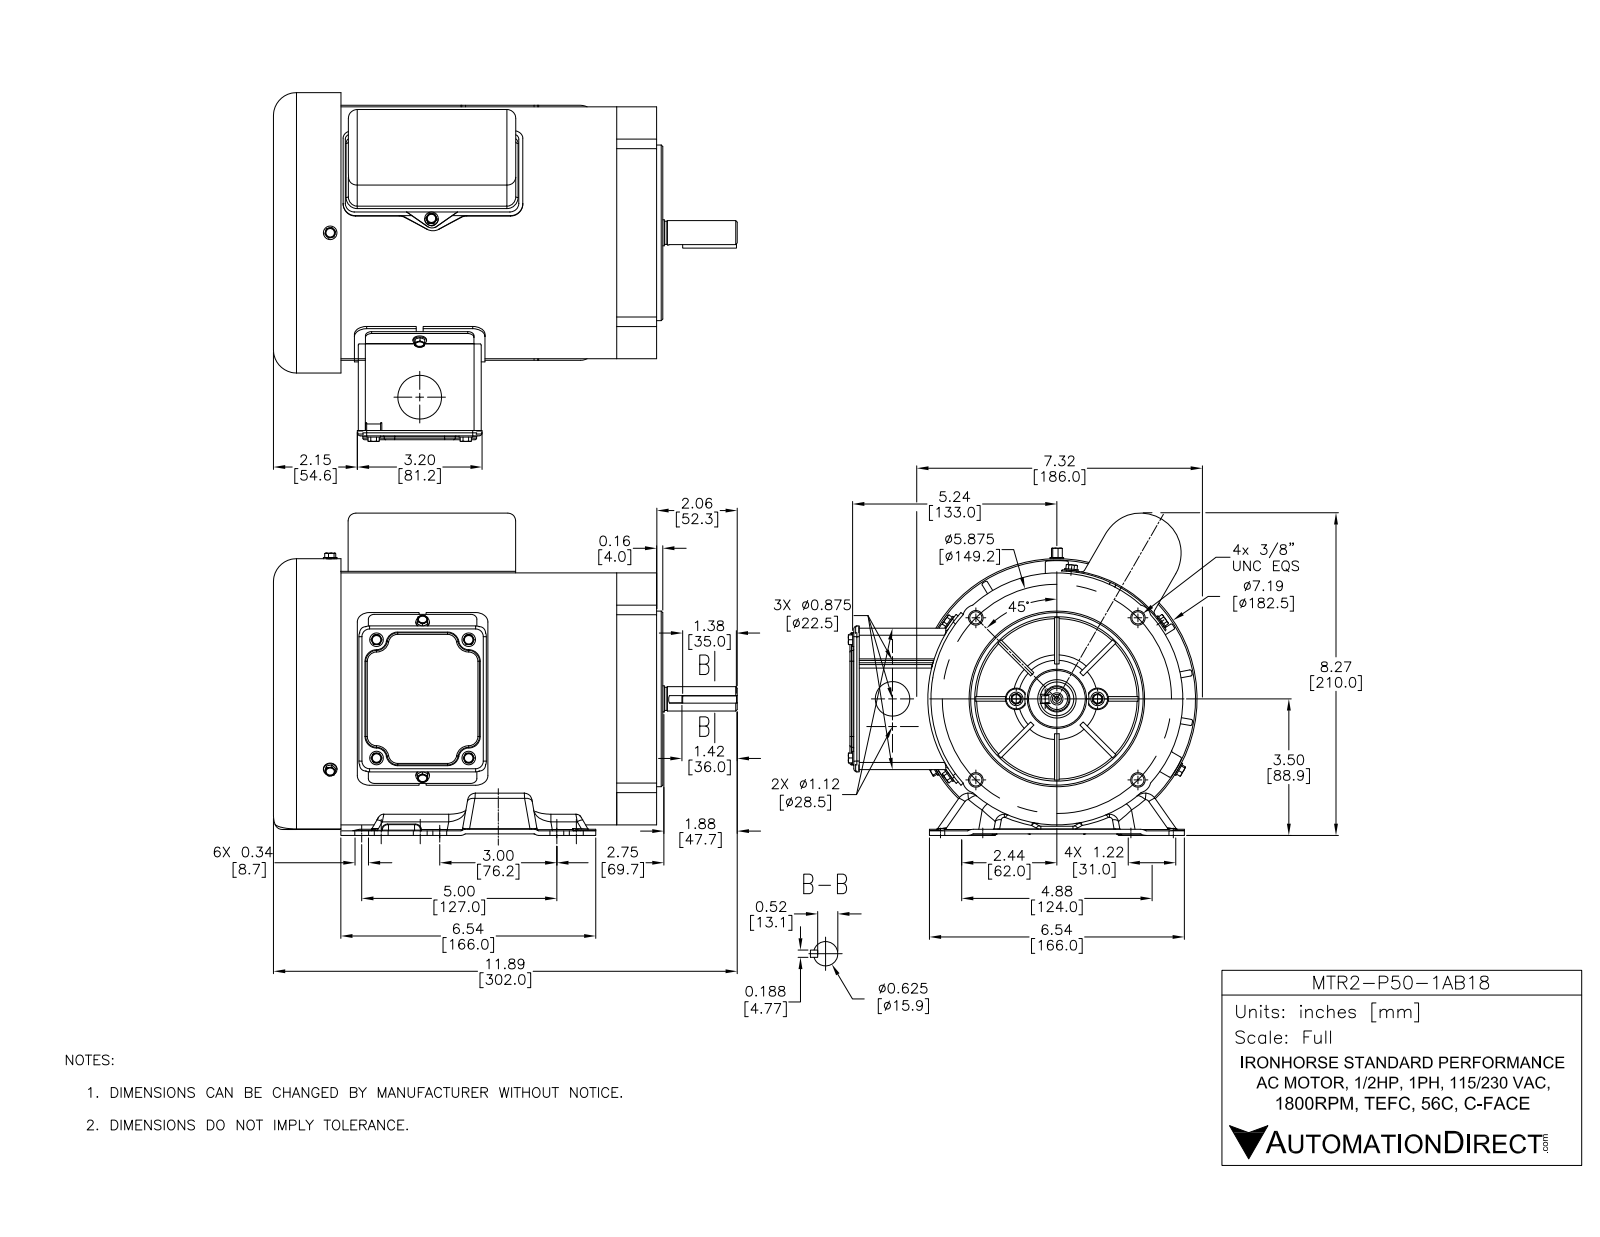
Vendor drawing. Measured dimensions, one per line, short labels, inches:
name: MTR2-P50-1AB18
written by: SolidWorks 2016 (AUTOMOTIVE_DESIGN)
unit: in
bodies: 40 solids, 2933 faces (827 planar, 938 cylindrical, 1168 other)
size: 11.634 × 8.938 × 8.3
volume: 46.18 in³; area: 1 045 in²
holes: 12× ⌀0.197, 11× ⌀0.219, 8× ⌀0.276, 6× ⌀0.217, 6× ⌀0.344, 5× ⌀0.136, 4× ⌀0.15, 4× ⌀0.177, 4× ⌀0.313, 3× ⌀0.709, 2× ⌀0.13, 2× ⌀0.134
bosses: 11× ⌀0.164, 7× ⌀0.348, 6× ⌀0.25, 4× ⌀0.348, 2× ⌀0.414, 2× ⌀0.19, 1× ⌀7.185, 1× ⌀6.457
rounds: 125× R0.118, 38× R0.039, 32× R0.157, 30× R0.02, 26× R0.138, 20× R0.228, 19× R0.276, 17× R0.197
face distances: 0.118, 0.039, 0.063, 8.386, 1.024, 1.142, 9.567, 9.528, 0.047, 3.087
hole spacings: 4.221, 3.031, 0.094, 2.32, 2.409, 2.937, 2.979, 3.748
